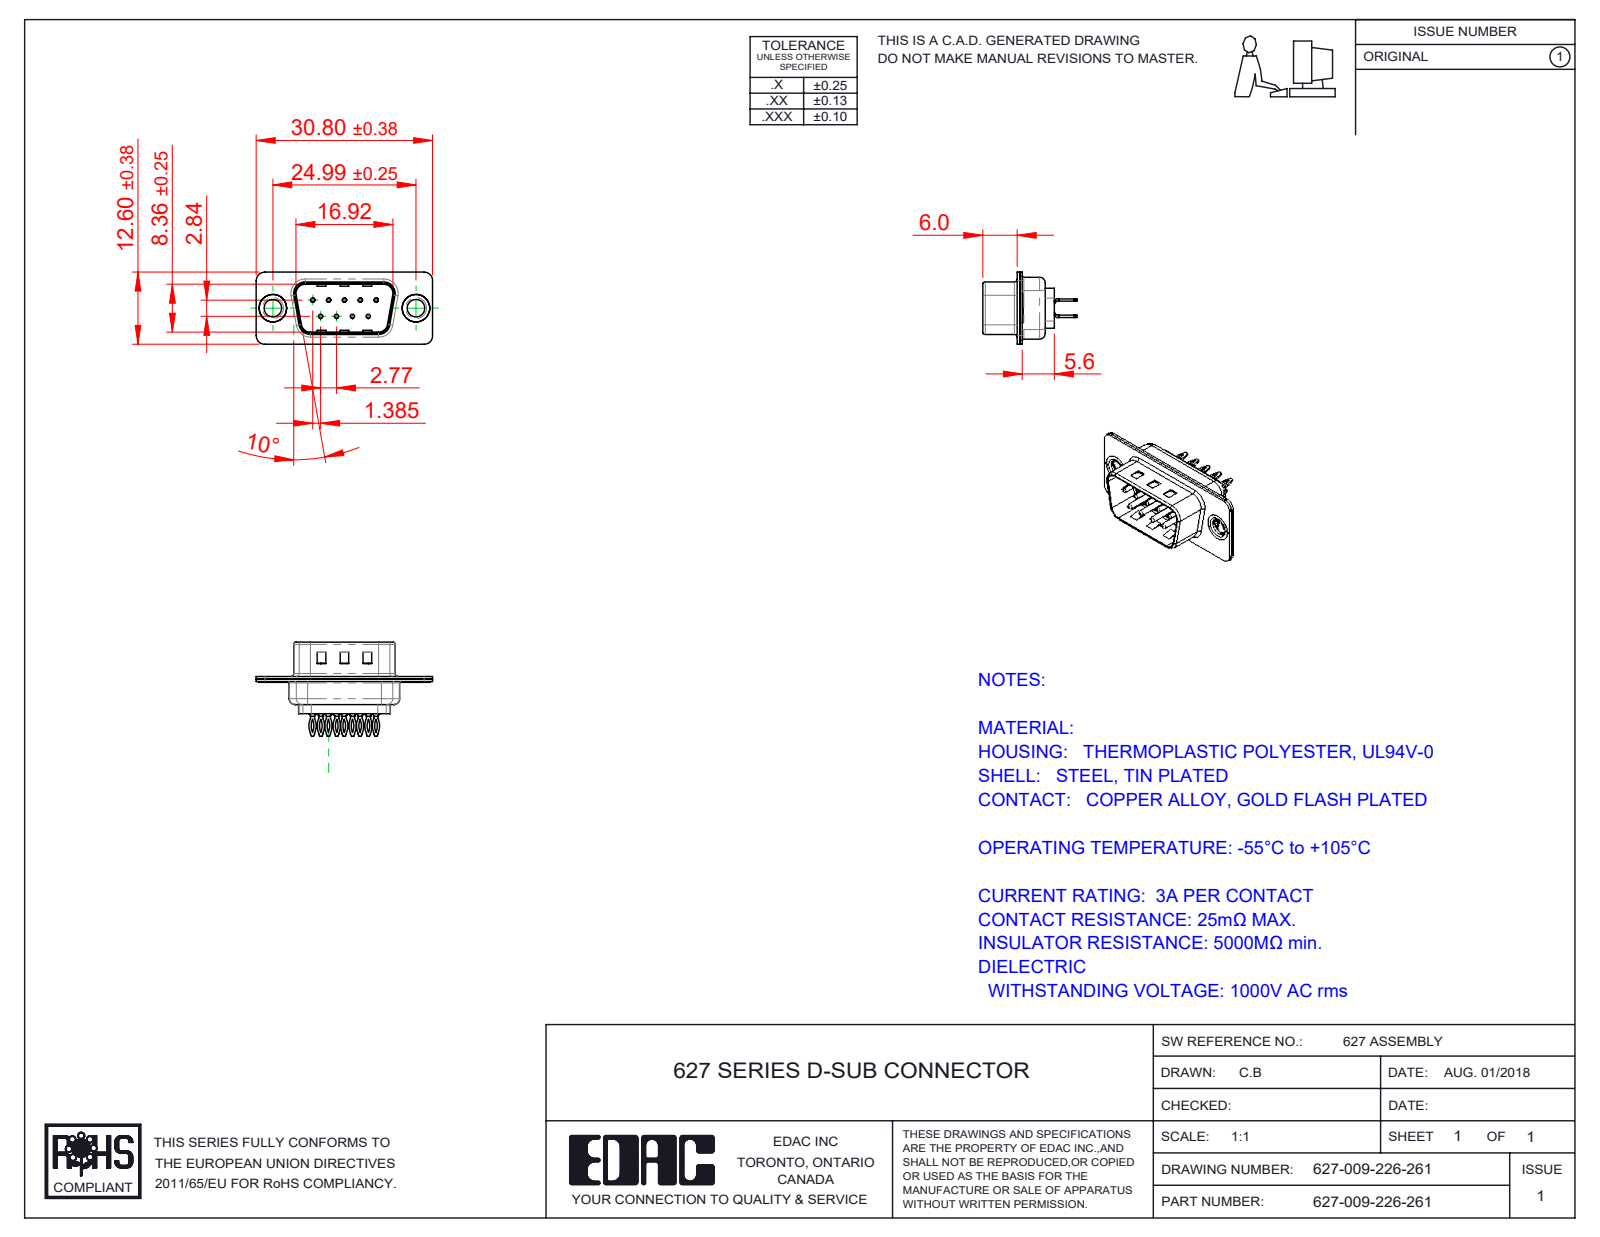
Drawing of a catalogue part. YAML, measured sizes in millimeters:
part_name: "627 Contact Row 1_26L; 627 Housing_09 LP; 627 Shell Front_09 Contacts; 627-009-226-061 (+3 more)"
step_written_by: "SolidWorks 2020 (CONFIG_CONTROL_DESIGN)"
units: millimeters
bodies: {solids: 14, faces: 962, planar: 287, cylindrical: 392, other: 283}
overall_size: [30.8, 16.45, 12.6]
volume: 1234
surface_area: 3761
round_holes:
  - {diameter: 0.35, count: 9}
  - {diameter: 1.1, count: 9}
  - {diameter: 1.6, count: 9}
  - {diameter: 3.05, count: 2}
  - {diameter: 4, count: 2}
  - {diameter: 4.8, count: 2}
round_bosses_or_shafts:
  - {diameter: 2, count: 9}
  - {diameter: 1.5, count: 9}
  - {diameter: 0.75, count: 9}
  - {diameter: 5, count: 2}
  - {diameter: 4.9, count: 2}
  - {diameter: 3.55, count: 2}
partial_cylinders:
  - {radius: 1.5, count: 18}
  - {radius: 2.92, count: 18}
  - {radius: 3.33, count: 18}
  - {radius: 2, count: 12}
  - {radius: 0.5, count: 8}
  - {radius: 1.6, count: 8}
  - {radius: 0.25, count: 4}
  - {radius: 0.6, count: 4}
face_to_face_distances: [0.4, 0.45, 0.9, 0.82, 9.58, 1.4, 0.5, 8.76, 1.5, 6.05]
hole_center_spacings: [3.16, 2.77, 5.54, 5.03, 5.04, 8.31, 7.48, 7.49]
